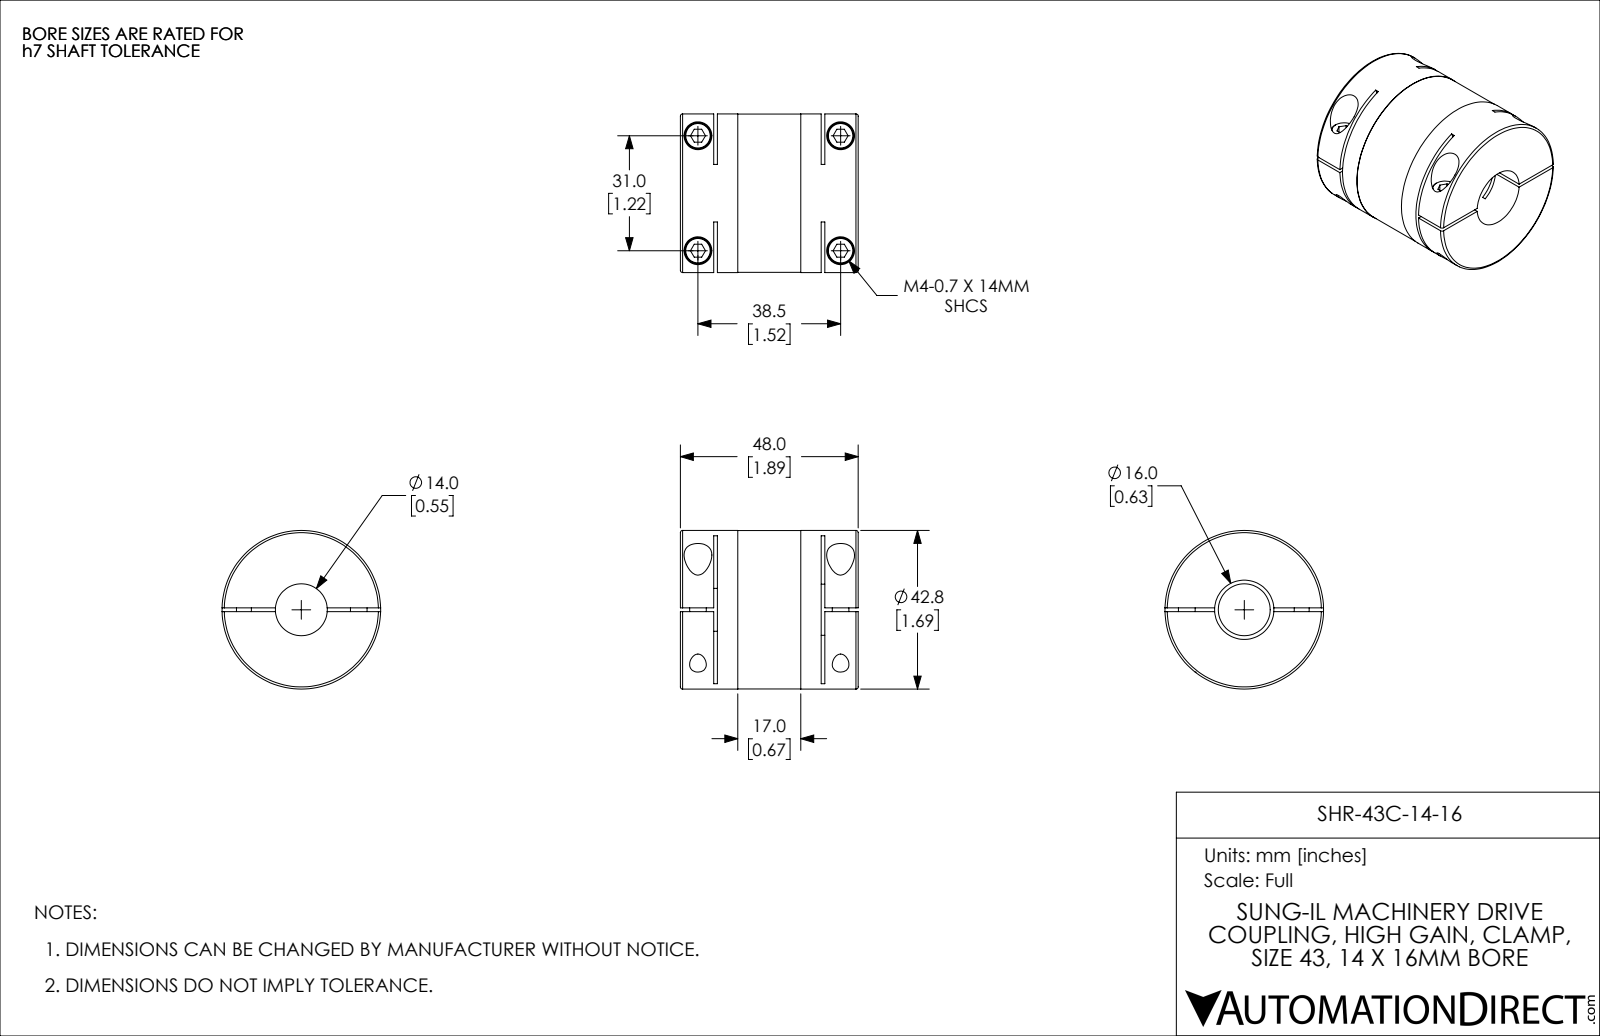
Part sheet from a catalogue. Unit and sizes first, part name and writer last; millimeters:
Units: millimetres
Overall size (bounding box): 48 × 42.8 × 42.8
Round holes (diameter × count): ⌀4.5 ×4, ⌀7.5 ×4, ⌀14 ×1, ⌀16 ×1, ⌀18 ×1
Round bosses / shafts (diameter × count): ⌀7 ×4, ⌀4 ×2, ⌀42.8 ×1, ⌀42.7 ×1
Partial cylindrical surfaces — rounded edges, fillets, slot ends (radius × count): R50 ×2
Main face-to-face distances: 1, 10, 38, 9, 39, 29, 48, 28, 30, 15.5
Hole centre spacings: 31, 38.5, 49.43
Volume: 55 257 mm³ · Surface area: 18 076 mm²
Bodies: 1 solid, 144 faces (70 planar, 58 cylindrical, 16 other)
Part name (STEP PRODUCT): SHR-43C-14-16
STEP written by: SolidWorks 2021 (CONFIG_CONTROL_DESIGN)
